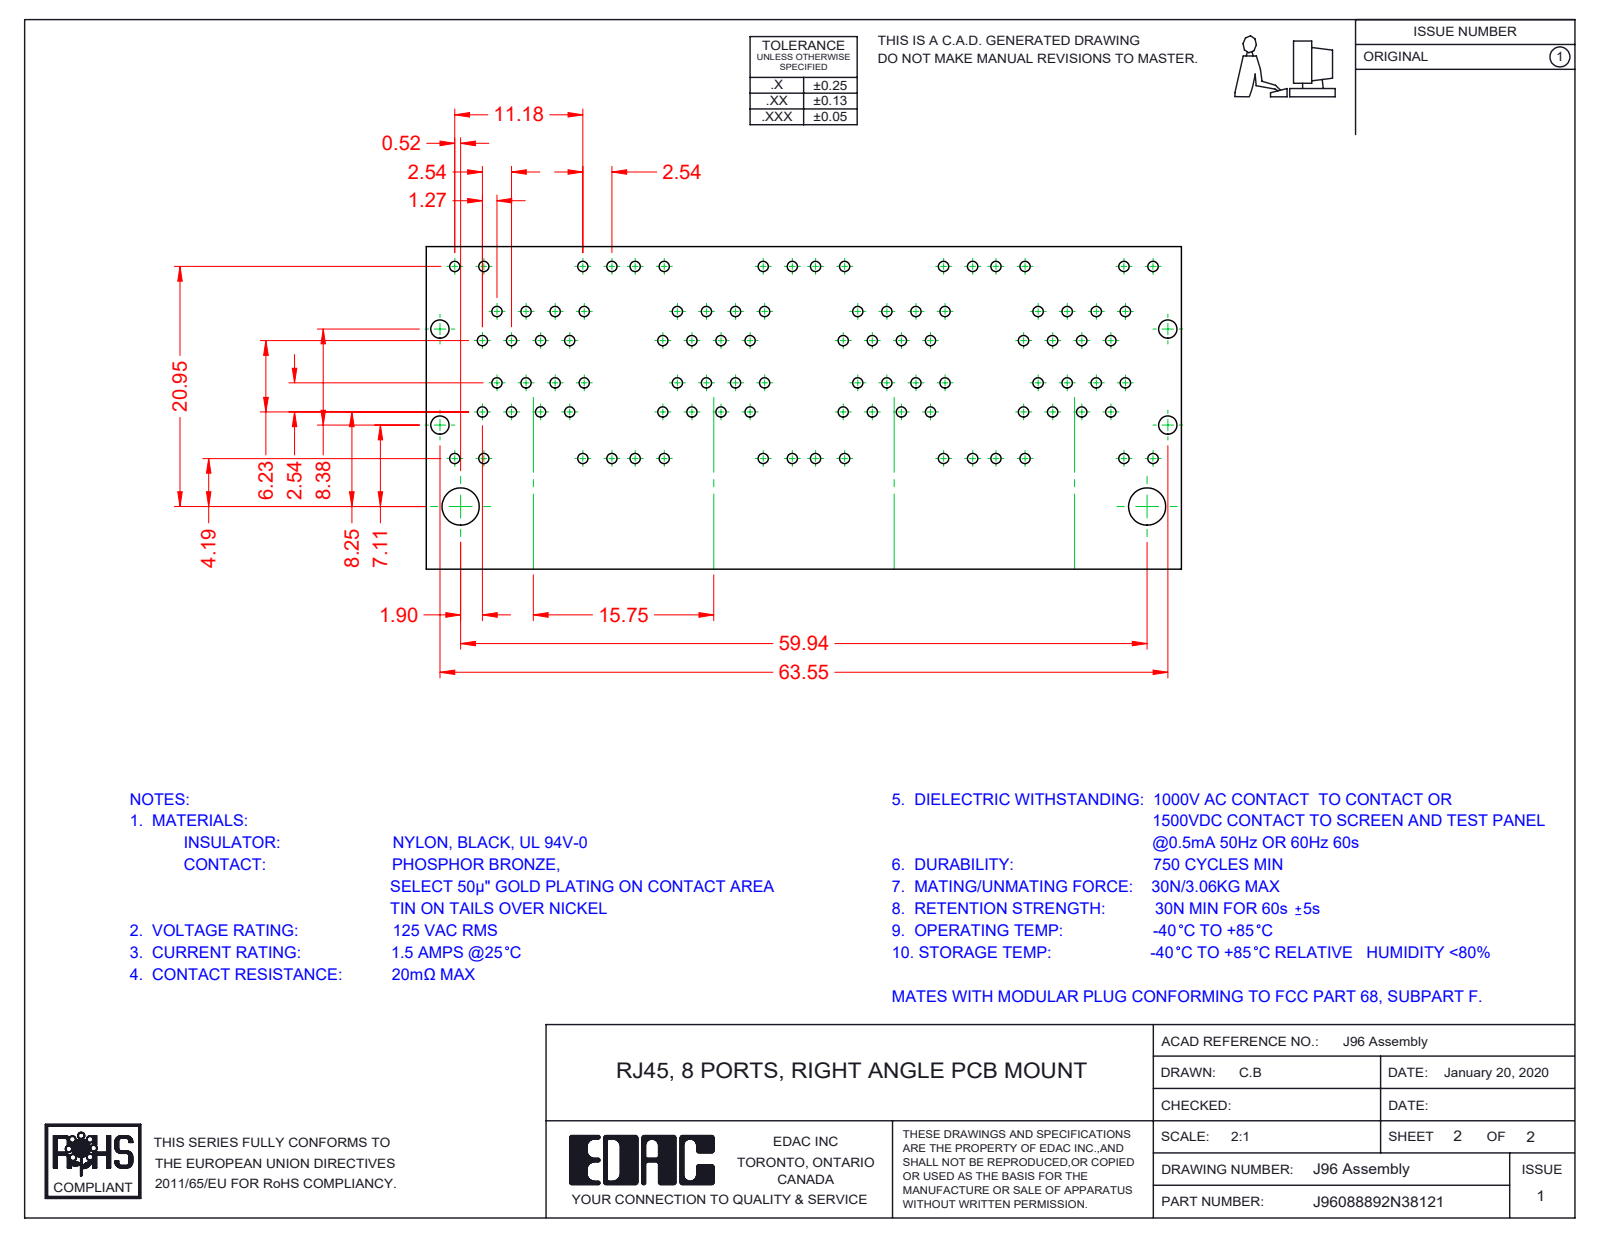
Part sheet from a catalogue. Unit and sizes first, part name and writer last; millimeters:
Units: millimetres
Overall size (bounding box): 64.05 × 29.58 × 28.68
Round holes (diameter × count): ⌀1.7 ×3
Round bosses / shafts (diameter × count): ⌀1.68 ×3
Partial cylindrical surfaces — rounded edges, fillets, slot ends (radius × count): R0.25 ×124, R0.35 ×73, R1 ×72, R0.5 ×49, R0.91 ×32, R0.2 ×21, R0.7 ×11, R0.22 ×8
Main face-to-face distances: 15.75, 0.35, 9.95, 1.17, 1.6, 0.54, 9.98, 10.18, 12.67, 3.37
Hole centre spacings: 15.75, 31.5
Volume: 24 160 mm³ · Surface area: 63 658 mm²
Bodies: 96 solids, 7658 faces (6069 planar, 1323 cylindrical, 266 other)
Part name (STEP PRODUCT): 96 LED RH Lower_8-Red-Yellow; 96 LED LH Upper_3-Green; 96 Contact Lock Lower; 96 Insulator Insert (+8 more)
STEP written by: SolidWorks 2016 (CONFIG_CONTROL_DESIGN)
